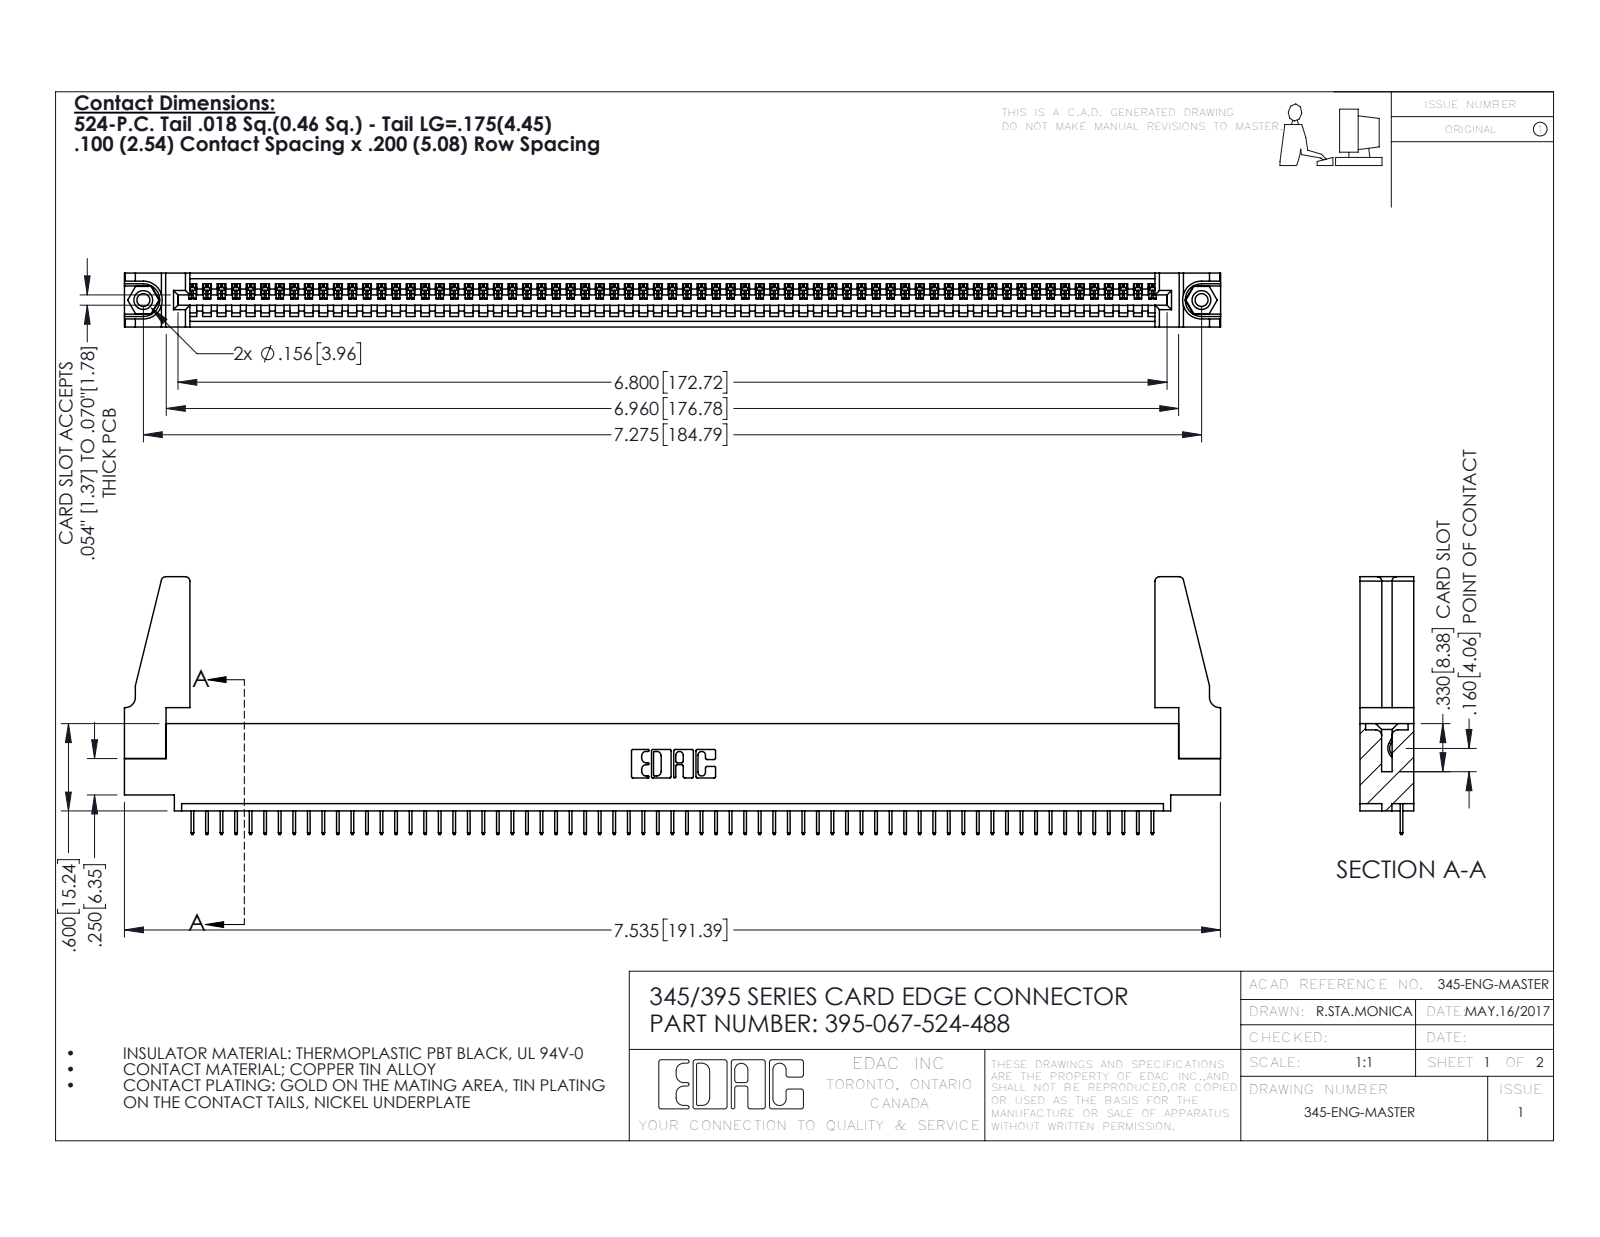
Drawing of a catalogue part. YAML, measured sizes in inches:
part_name: "395-067-524-488; 345-220-078_345-220-088; 345-292-001_345-293-124; 345-250-001_345-250-001-102 (+1 more)"
step_written_by: "SolidWorks 2016 (CONFIG_CONTROL_DESIGN)"
units: inches
bodies: {solids: 72, faces: 4408, planar: 3238, cylindrical: 1154, other: 16}
overall_size: [7.536, 1.772, 0.37]
volume: 1.3
surface_area: 41.37
round_holes:
  - {diameter: 0.089, count: 2}
  - {diameter: 0.125, count: 2}
  - {diameter: 0.156, count: 2}
  - {diameter: 0.064, count: 1}
round_bosses_or_shafts:
  - {diameter: 0.155, count: 2}
partial_cylinders:
  - {radius: 0.006, count: 134}
  - {radius: 0.01, count: 22}
  - {radius: 0.03, count: 8}
  - {radius: 0.007, count: 6}
  - {radius: 0.031, count: 6}
  - {radius: 0.026, count: 3}
  - {radius: 0.031, count: 2}
  - {radius: 0.04, count: 2}
face_to_face_distances: [0.072, 0.298, 0.37, 0.098, 0.272, 0.025, 0.2, 0.225, 0.072, 0.149]
hole_center_spacings: [0.27, 7.039, 7.275]
